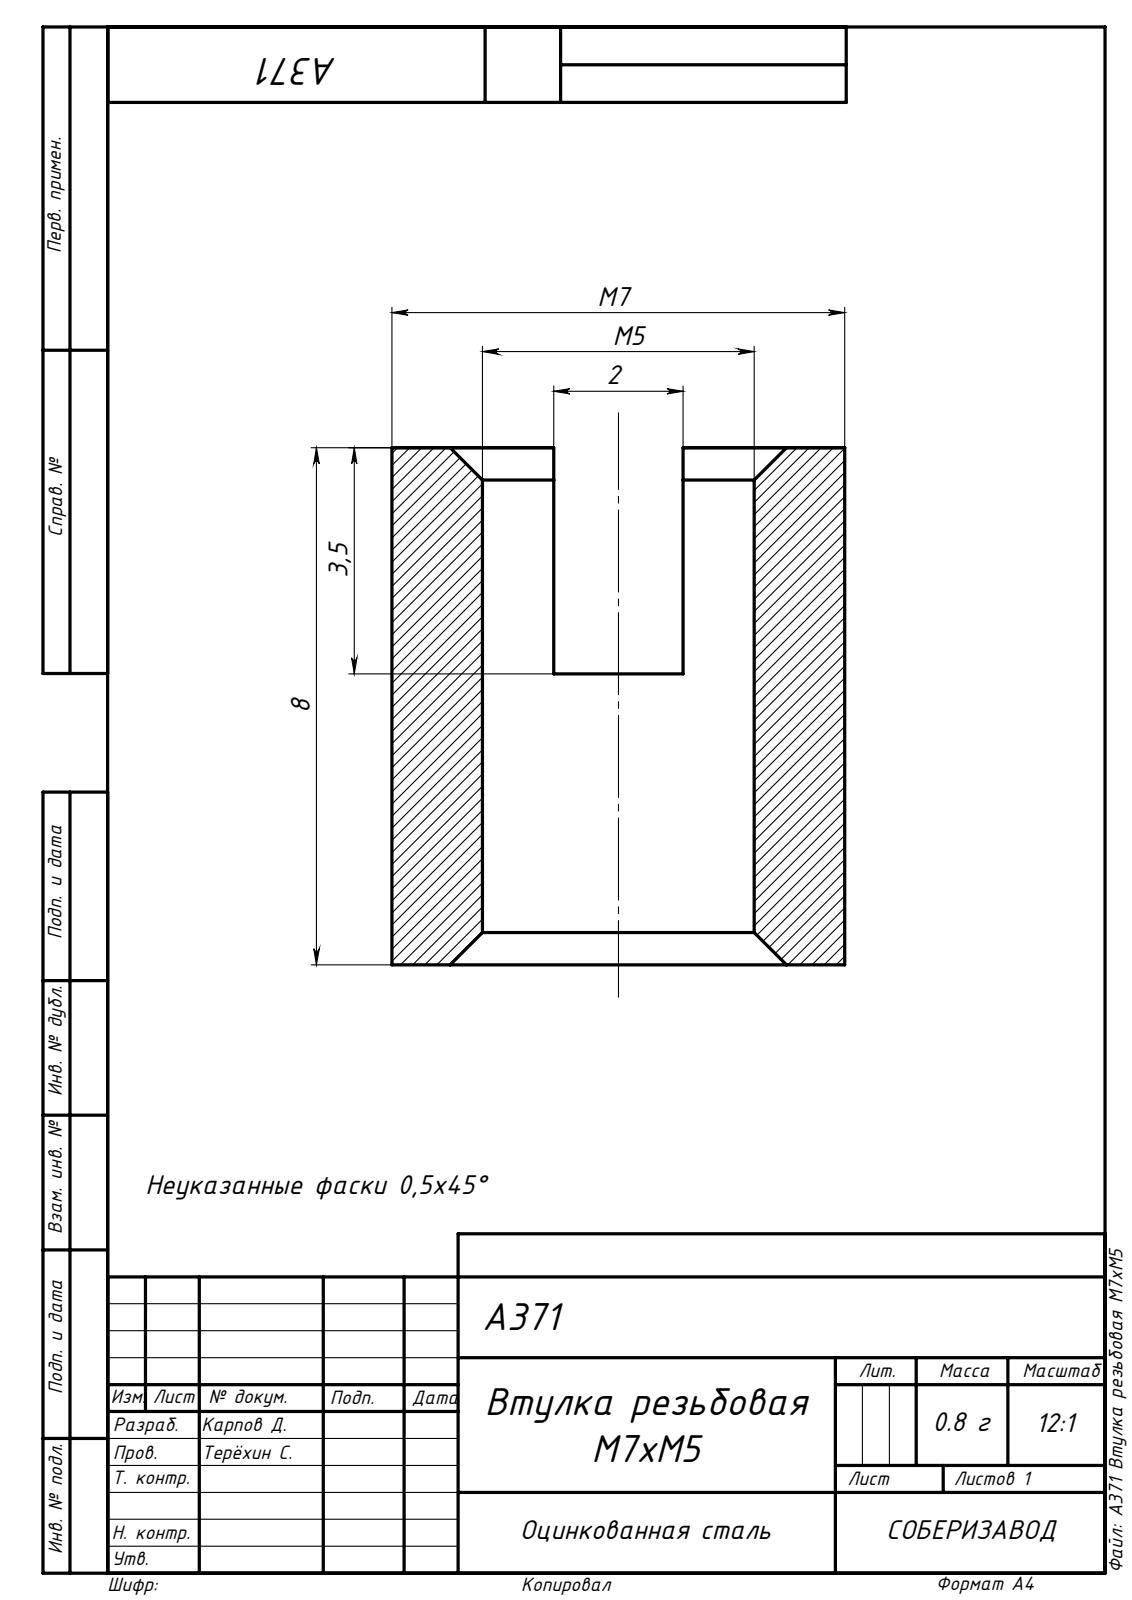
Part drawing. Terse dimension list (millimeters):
name: A371 Втулка резьбовая M7xM5
written by: SolidWorks 2019 (AUTOMOTIVE_DESIGN)
unit: mm
bodies: 1 solid, 17 faces (9 planar, 4 cylindrical, 4 other)
size: 8 × 7 × 7
volume: 174 mm³; area: 317 mm²
holes: 1× ⌀4.2
bosses: 1× ⌀7
face distances: 8, 2, 4.5, 3.5
